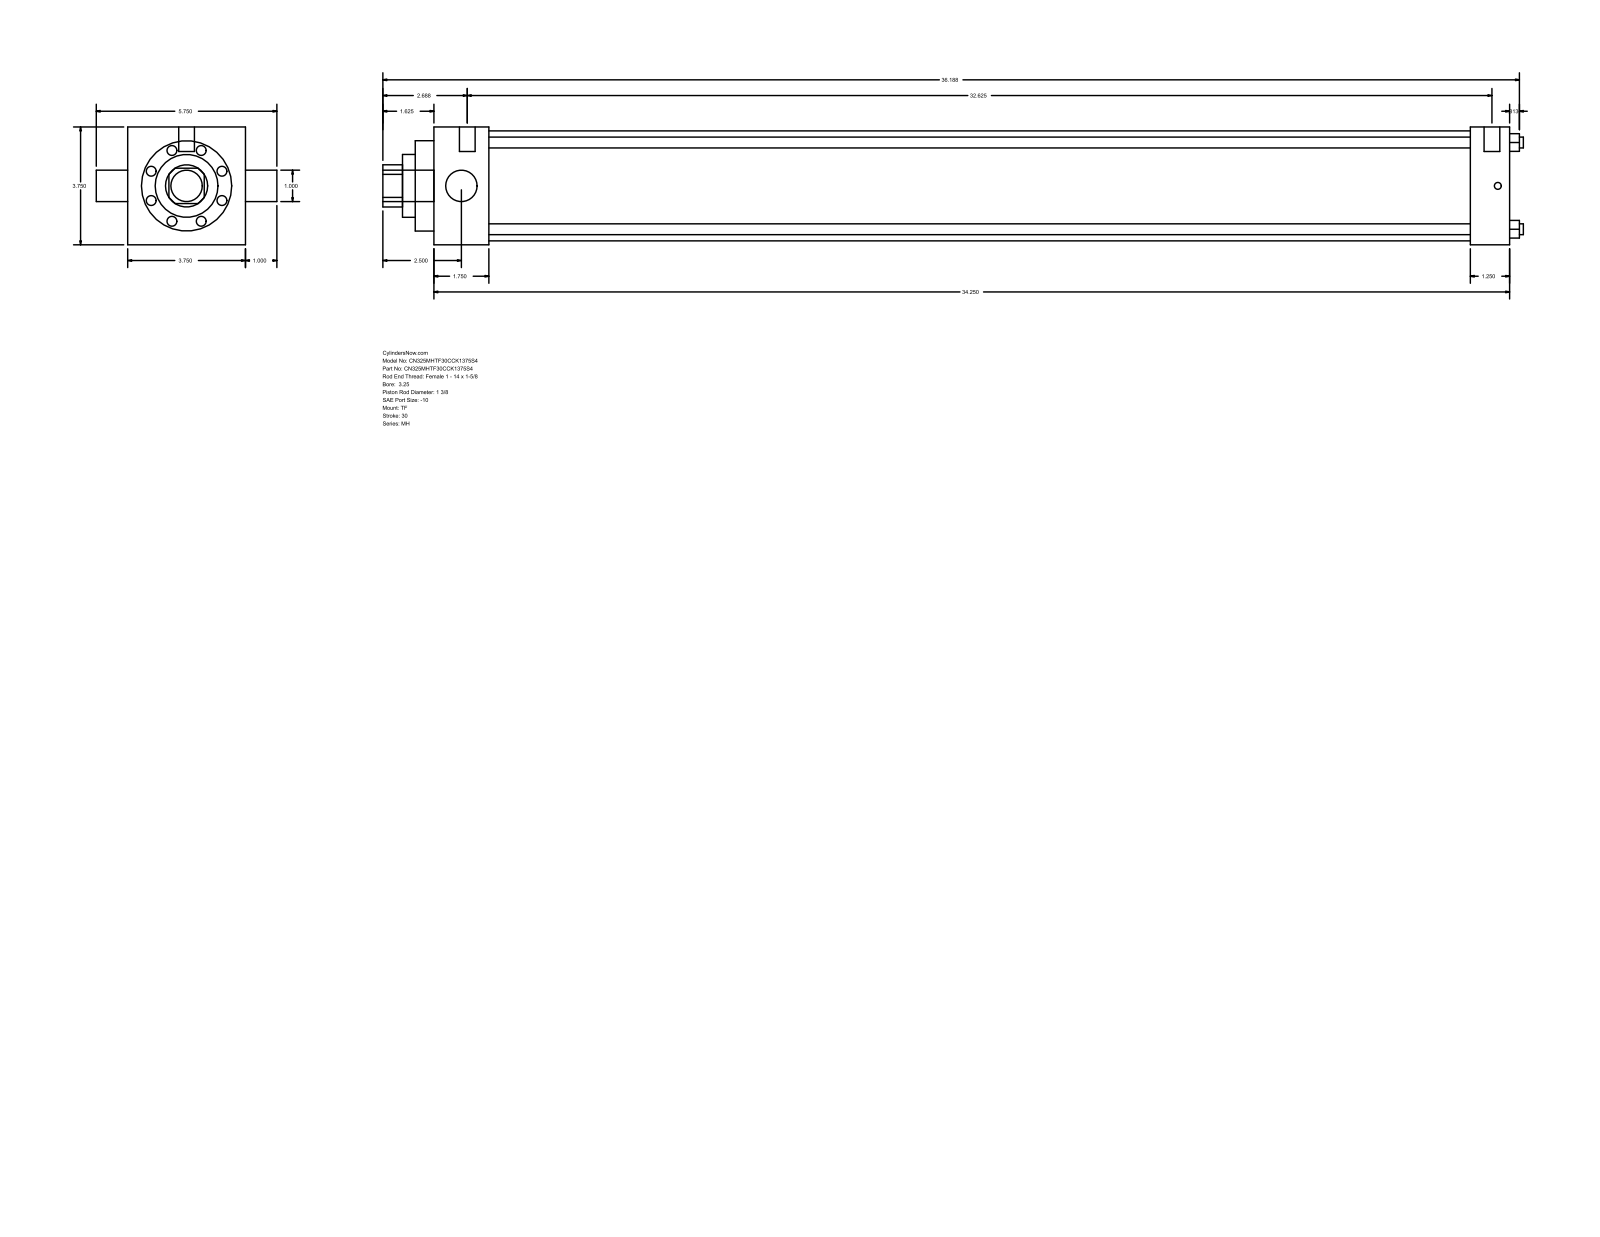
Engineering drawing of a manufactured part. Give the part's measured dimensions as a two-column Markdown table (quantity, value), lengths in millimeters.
| quantity | value |
| --- | --- |
| part name | MH_TF__0325_1.375 |
| STEP written by | GSSL Pune (CONFIG_CONTROL_DESIGN) |
| units | millimeters |
| bodies | 0 solids, 86 faces (61 planar, 25 cylindrical, 0 other) |
| overall size | 922.34 × 146.05 × 95.25 |
| round holes (diameter × count) | 8.76 × 4, 25.4 × 1, 34.92 × 1, 50.8 × 1, 73.03 × 1, 88.9 × 1 |
| round bosses / shafts (diameter × count) | 5.56 × 3, 12.7 × 2, 25.4 × 1 |
| partial cylindrical surfaces (radius × count) | 17.06 × 1 |
| main face-to-face distances | 95.24, 869.96, 44.45, 838.21, 793.76, 825.51, 31.75, 15.08, 59.53, 853.29 |
| hole center spacings | 49.57, 70.1, 99.14 |
